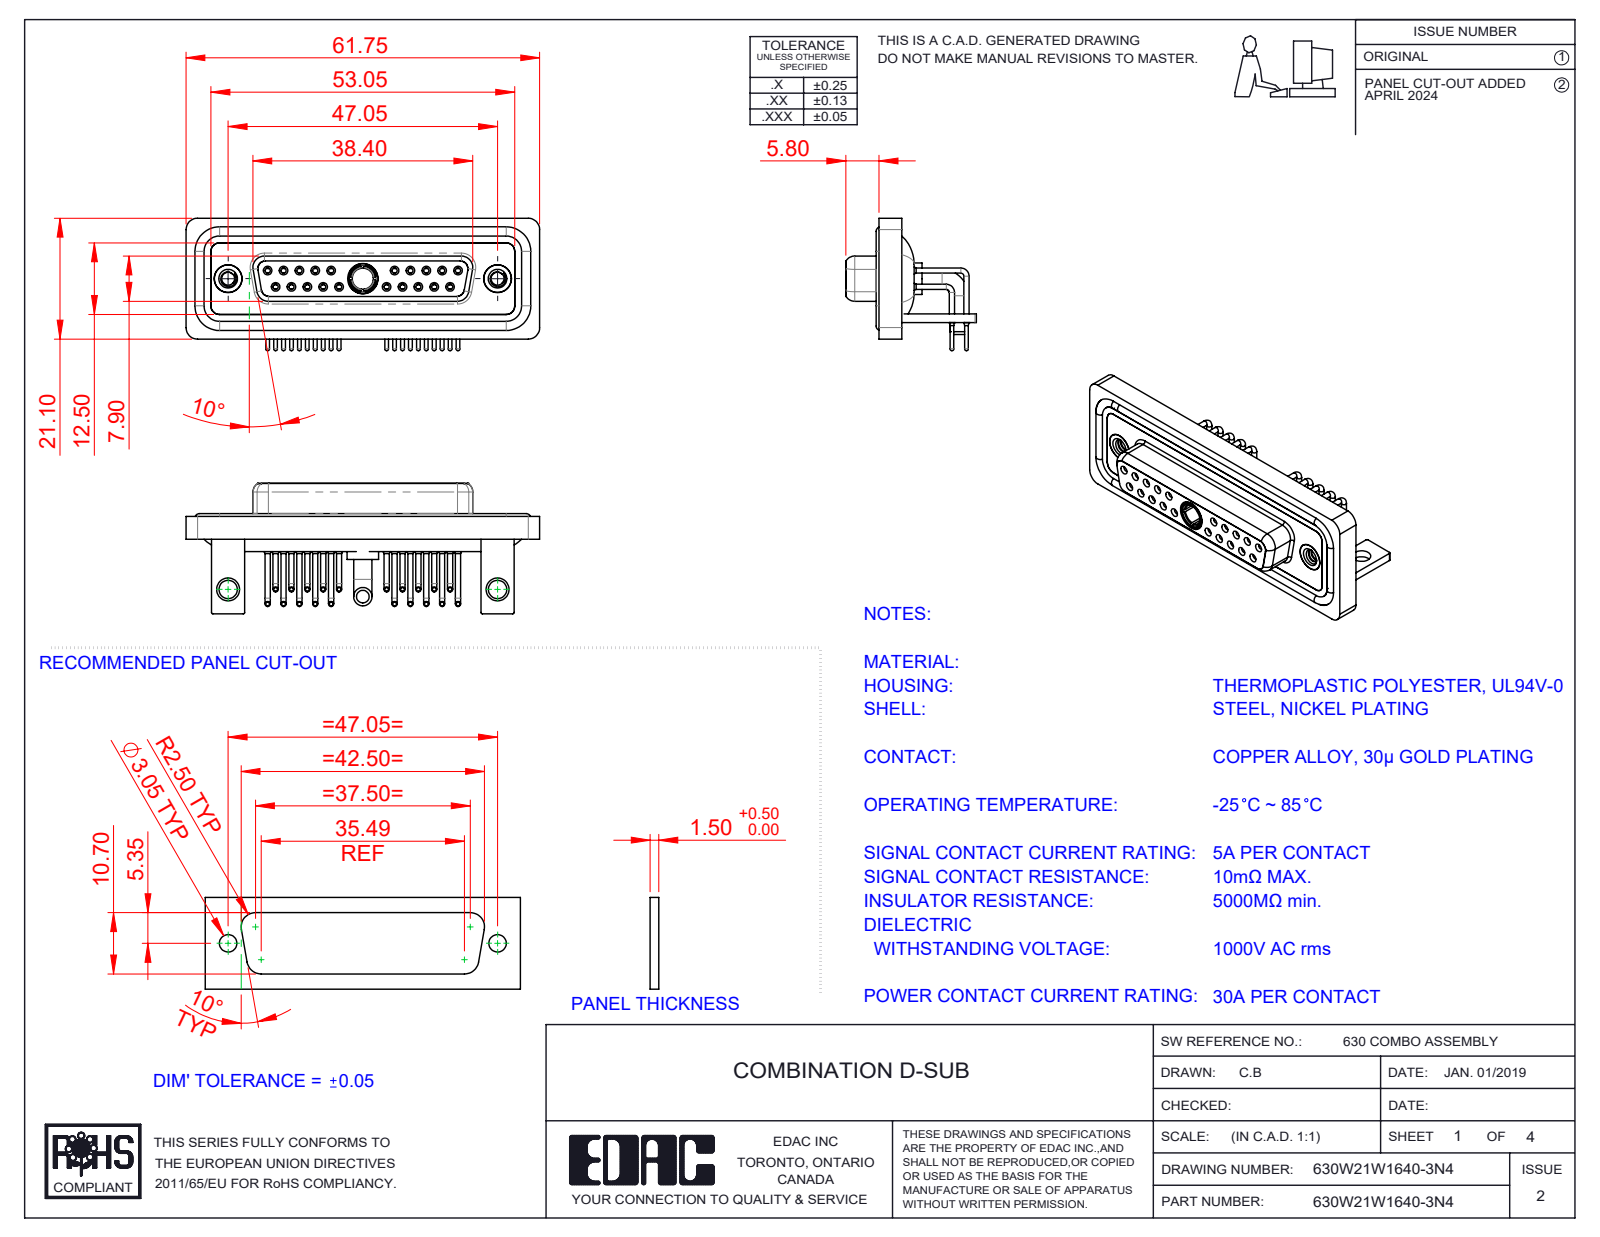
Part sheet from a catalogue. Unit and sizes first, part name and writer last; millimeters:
Units: millimetres
Overall size (bounding box): 61.75 × 23.12 × 22.8
Round holes (diameter × count): ⌀0.9 ×20, ⌀1.1 ×20, ⌀1.5 ×20, ⌀2 ×20, ⌀1.6 ×10, ⌀1.7 ×10, ⌀4.85 ×3, ⌀2.26 ×2, ⌀3.2 ×2, ⌀4 ×2, ⌀4.05 ×2, ⌀5 ×2
Round bosses / shafts (diameter × count): ⌀0.9 ×20, ⌀0.65 ×20, ⌀1.6 ×14, ⌀4.95 ×2, ⌀4.8 ×2, ⌀3.2 ×2, ⌀5.5 ×1, ⌀5.2 ×1
Partial cylindrical surfaces — rounded edges, fillets, slot ends (radius × count): R2 ×19, R1.5 ×18, R0.25 ×16, R1.35 ×8, R1.6 ×8, R0.5 ×5, R0.6 ×4, R0.65 ×4
Main face-to-face distances: 0.4, 1.8, 2.9, 3.7, 1.5, 4.1, 1.1, 1.4, 1.6, 2.5
Hole centre spacings: 3.16, 2.77, 5.54, 8.31, 5.04, 19.39, 20.97, 22.16
Volume: 8 900 mm³ · Surface area: 15 533 mm²
Bodies: 31 solids, 1572 faces (454 planar, 697 cylindrical, 421 other)
Part name (STEP PRODUCT): 630Combo Waterproof Housing_25 Contacts; 630Combo Contact Row 1_50 Contacts; 630W21W1640-3N4; 630Combo Threaded Rivet_2 (+6 more)
STEP written by: SolidWorks 2023 (CONFIG_CONTROL_DESIGN)
